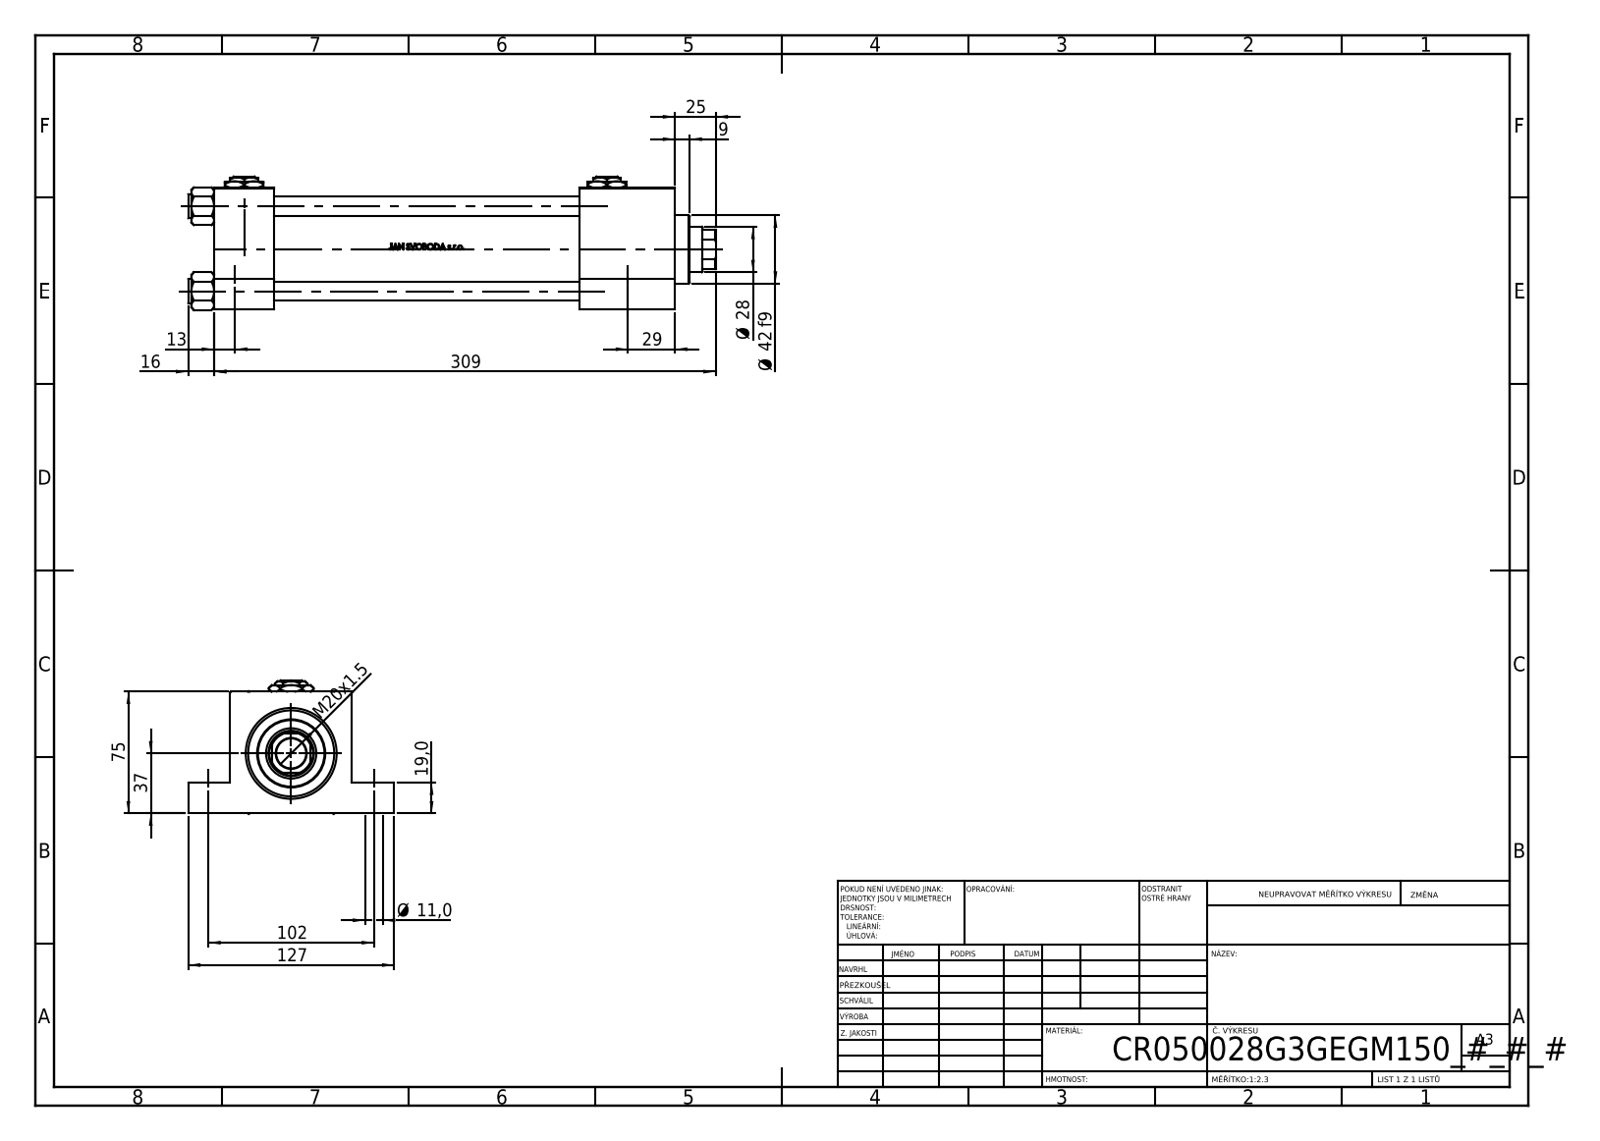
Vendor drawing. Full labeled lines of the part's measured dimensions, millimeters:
Part name (STEP PRODUCT): V215CR_G_TYCINKA; V215CR_G_Body; NUT_M5_G; V215_VC_A (+2 more)
STEP written by: SolidWorks 2019 (CONFIG_CONTROL_DESIGN)
Units: millimetres
Bodies: 13 solids, 1172 faces (476 planar, 124 cylindrical, 572 other)
Overall size (bounding box): 325 × 127 × 82.27
Volume: 977 141 mm³ · Surface area: 240 269 mm²
Round holes (diameter × count): ⌀11 ×4, ⌀12 ×4, ⌀7 ×2, ⌀20.96 ×2, ⌀30 ×2, ⌀18.5 ×1, ⌀28 ×1, ⌀31 ×1, ⌀41 ×1, ⌀50 ×1, ⌀53 ×1
Round bosses / shafts (diameter × count): ⌀15 ×4, ⌀56 ×1, ⌀42 ×1
Partial cylindrical surfaces — rounded edges, fillets, slot ends (radius × count): R13.5 ×1
Main face-to-face distances: 75, 37, 284, 247, 19, 56, 225, 188, 59, 26
Hole centre spacings: 52.3, 36.63, 37.34, 51.3, 52.63, 73.96, 102, 234.61
